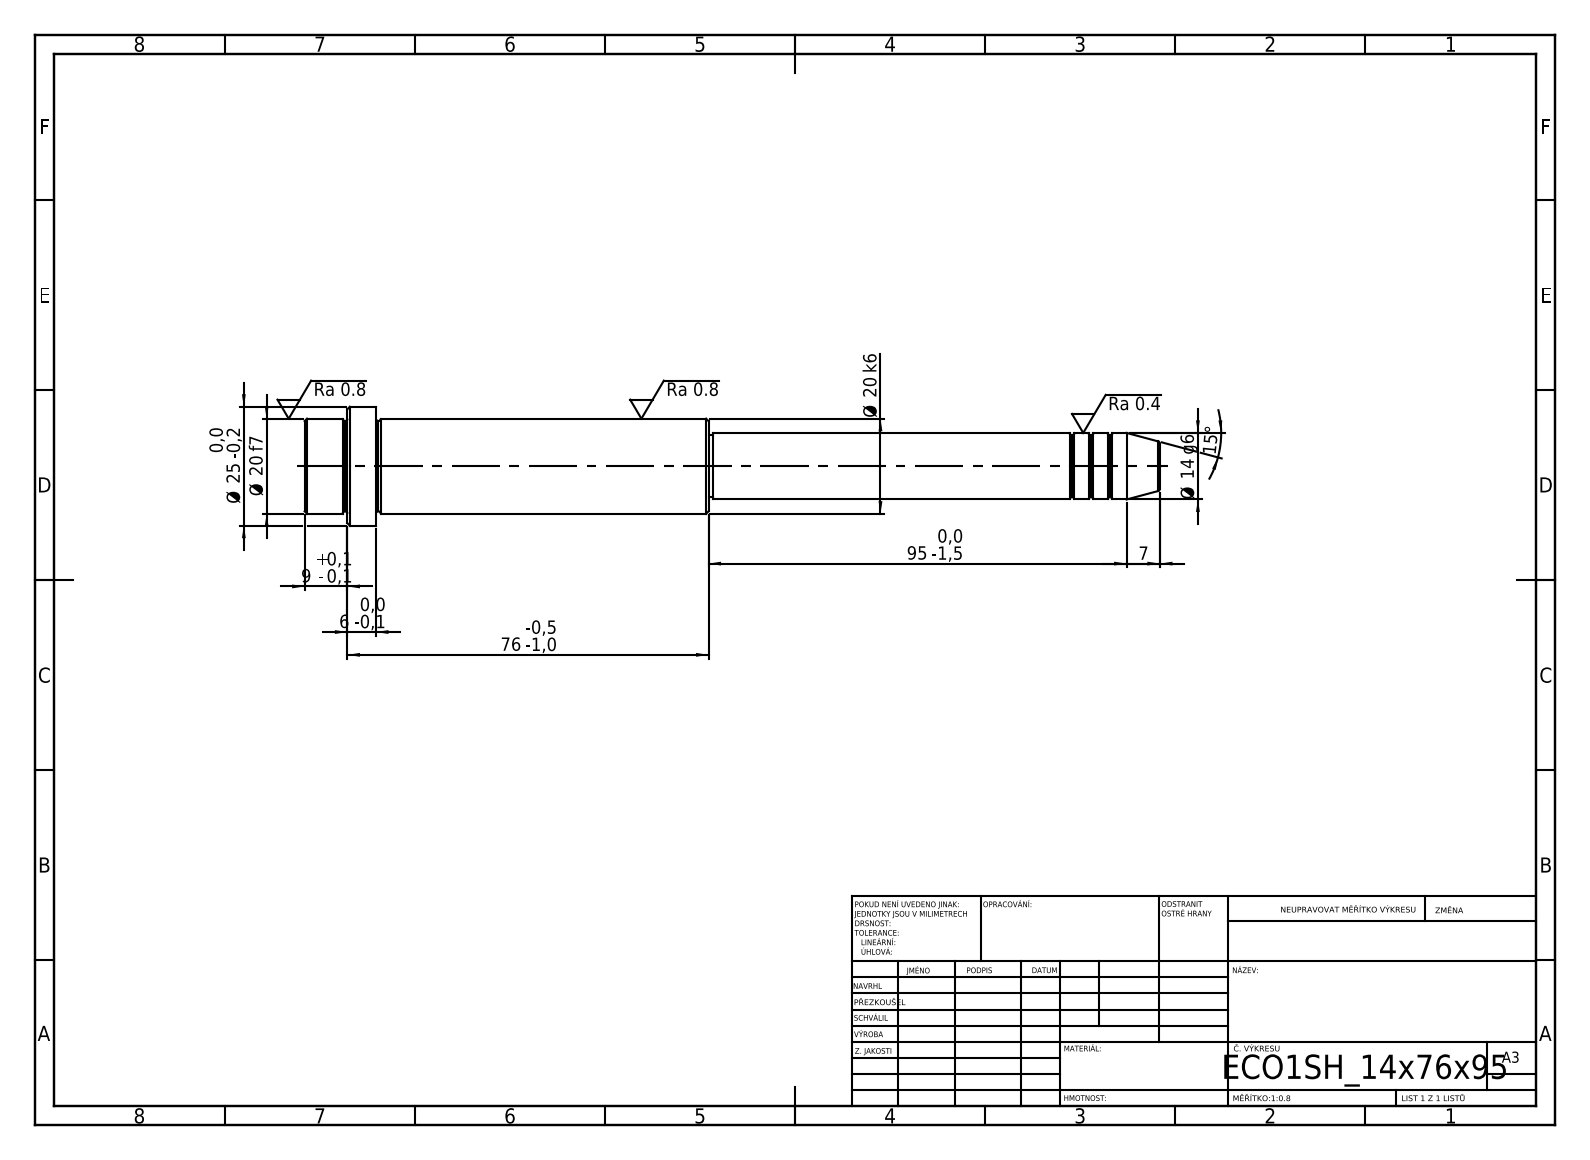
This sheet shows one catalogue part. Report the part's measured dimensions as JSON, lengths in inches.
{"step_written_by": "SolidWorks 2019 (CONFIG_CONTROL_DESIGN)", "units": "inches", "bodies": {"solids": 1, "faces": 52, "planar": 6, "cylindrical": 16, "other": 30}, "overall_size": [7.087, 0.984, 0.984], "volume_in3": 2.562, "surface_area_in2": 16.43, "round_bosses_or_shafts": [[0.984, 1], [0.787, 1], [0.551, 1], [0.512, 1]], "face_to_face_distances": [0.591, 2.756, 3.346, 2.992, 0.236, 0.354, 3.74, 6.496, 6.732, 7.087]}
